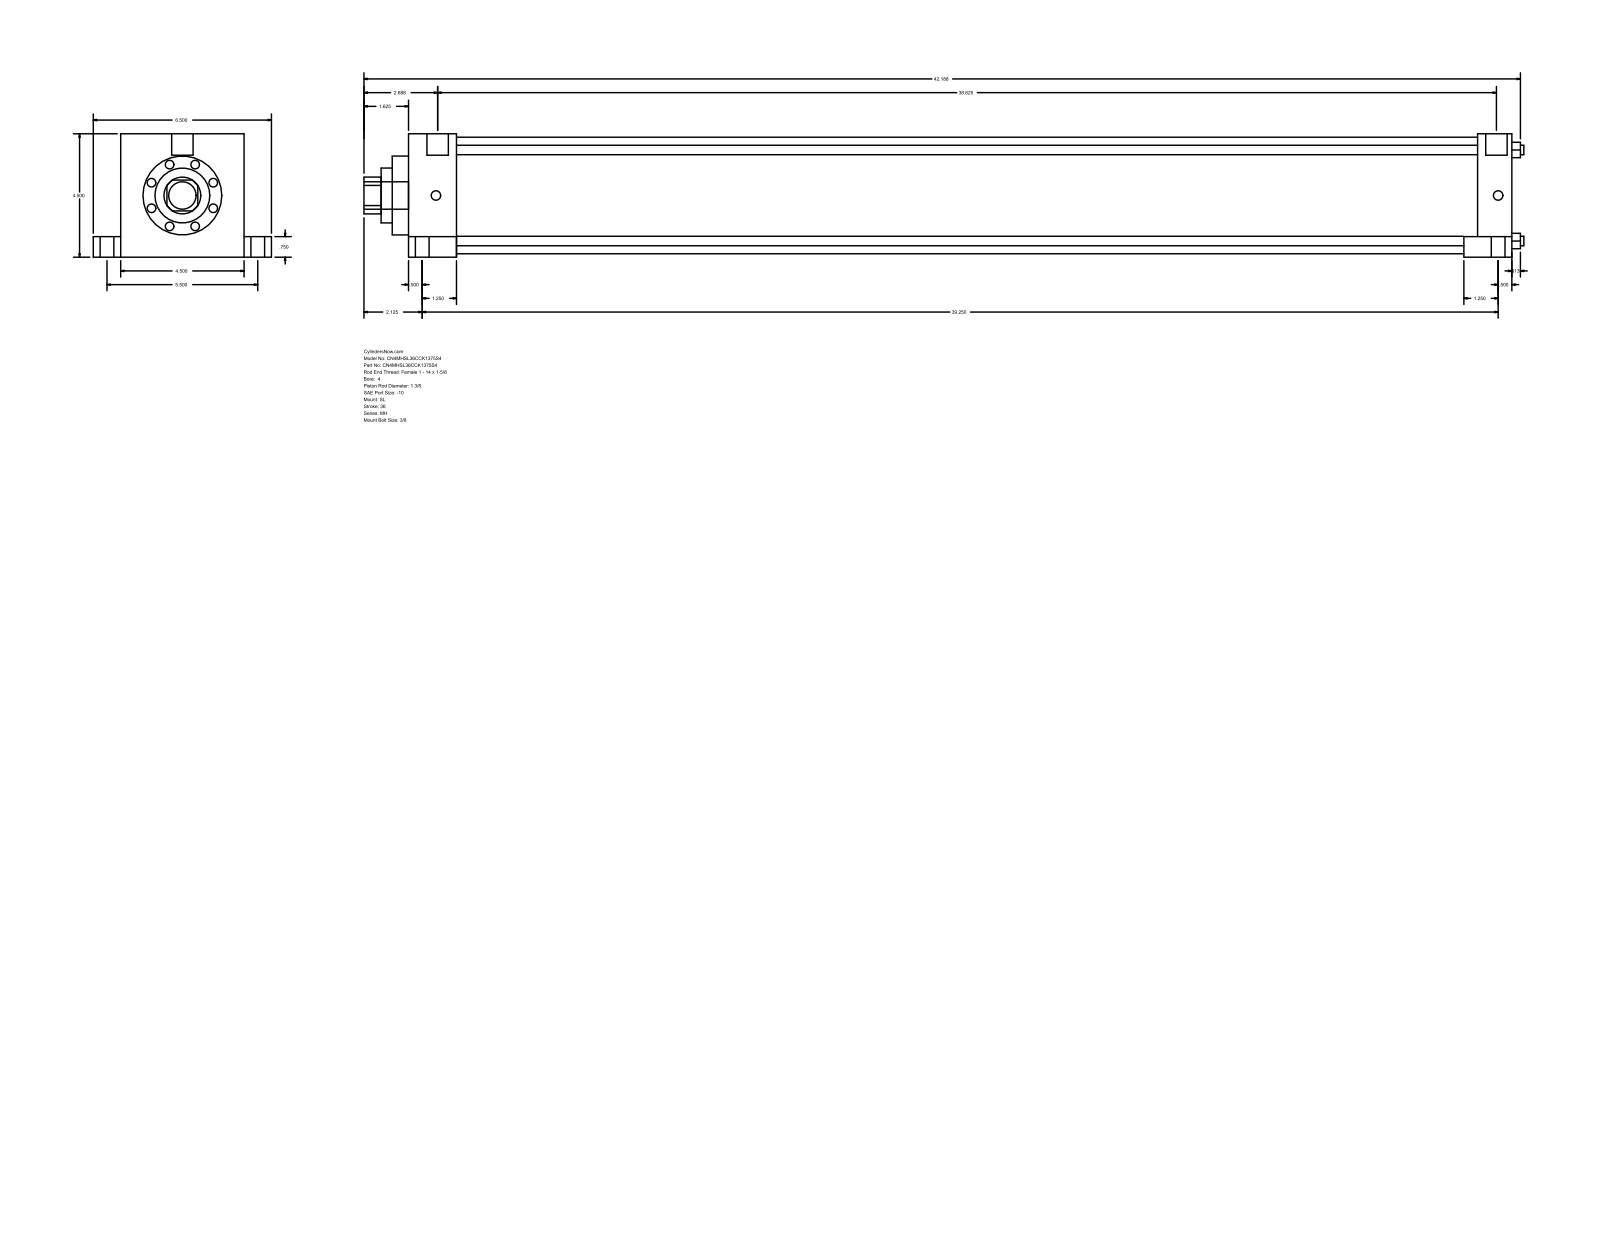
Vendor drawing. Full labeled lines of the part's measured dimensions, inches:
Part name (STEP PRODUCT): MH_SL__0400_1.375
STEP written by: GSSL Pune (CONFIG_CONTROL_DESIGN)
Units: inches
Bodies: 0 solids, 110 faces (77 planar, 33 cylindrical, 0 other)
Overall size (bounding box): 42.313 × 6.5 × 4.5
Round holes (diameter × count): ⌀0.345 ×4, ⌀1.375 ×1, ⌀2 ×1, ⌀2.875 ×1, ⌀4.25 ×1
Round bosses / shafts (diameter × count): ⌀0.75 ×4, ⌀0.5 ×4, ⌀0.344 ×4, ⌀0.781 ×2, ⌀1 ×1
Partial cylindrical surfaces — rounded edges, fillets, slot ends (radius × count): R0.672 ×1
Main face-to-face distances: 4.5, 40.25, 1.75, 38.5, 39, 37.25, 1.25, 1, 5.5, 0.75
Hole centre spacings: 2.347, 3.32, 4.695
